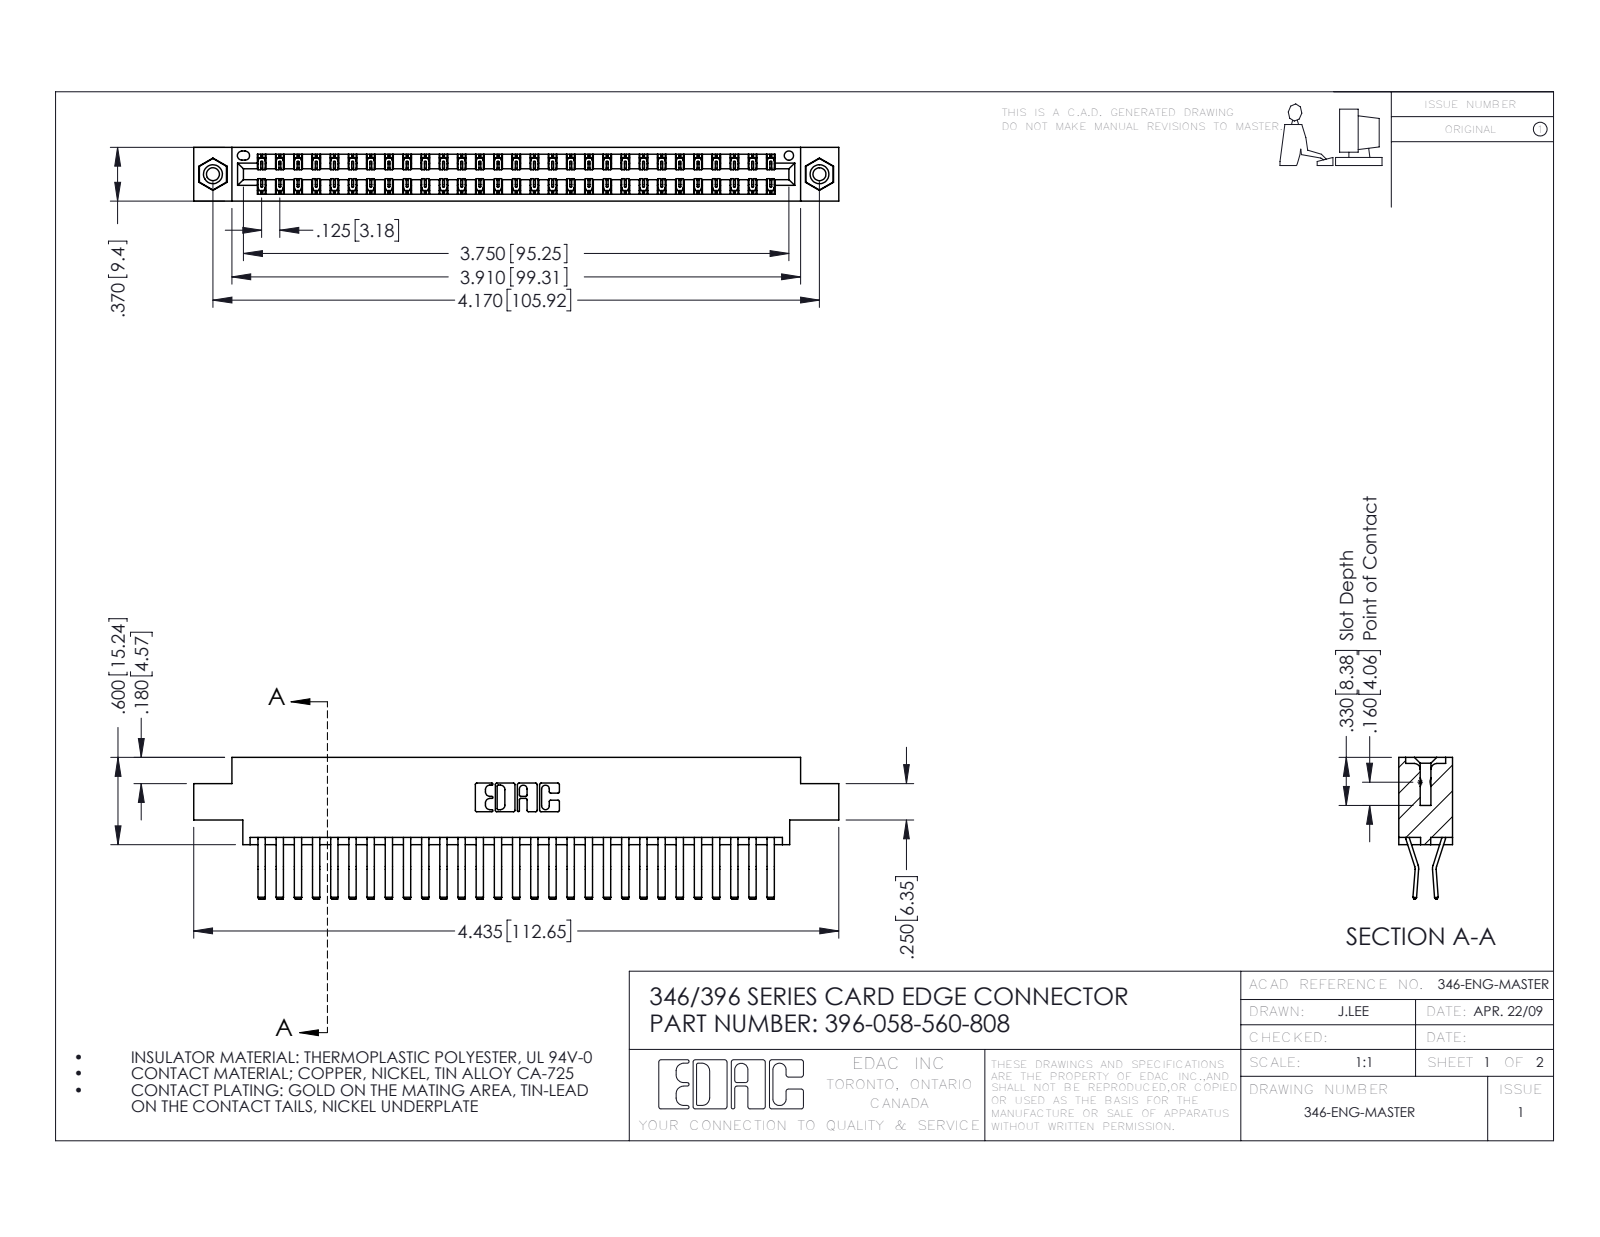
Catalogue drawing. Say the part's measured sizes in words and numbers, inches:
The part is named "345-292-001_560 Tail; 396-058-560-808; 345-250-001_345-250-003-102; 346 Part_0.170 Offset - 0.156 Dia-TI". Its 3-D file was written by "SolidWorks 2016 (CONFIG_CONTROL_DESIGN)". It is 61 solids with 3318 faces: 2142 planar, 1160 cylindrical and 16 other. Overall it measures 4.435 by 0.975 by 0.37 inches. Its volume is 0.678 cubic inches and its surface area 25.22 square inches. Round holes: 2 of diameter 0.089, 2 of diameter 0.125, 2 of diameter 0.156, 1 of diameter 0.064. Round bosses or shafts: 2 of diameter 0.155. Partial cylindrical surfaces (rounded edges, fillets, slot ends): 87 of radius 0.006, 22 of radius 0.01, 6 of radius 0.007, 6 of radius 0.031, 3 of radius 0.026, 2 of radius 0.01, 2 of radius 0.014, 2 of radius 0.022. The main face-to-face distances are 0.048, 0.322, 0.37, 0.025, 0.25, 0.072, 0.298, 0.275, 0.222, 0.148. The hole center spacings are 0.246, 3.962, 4.17.
